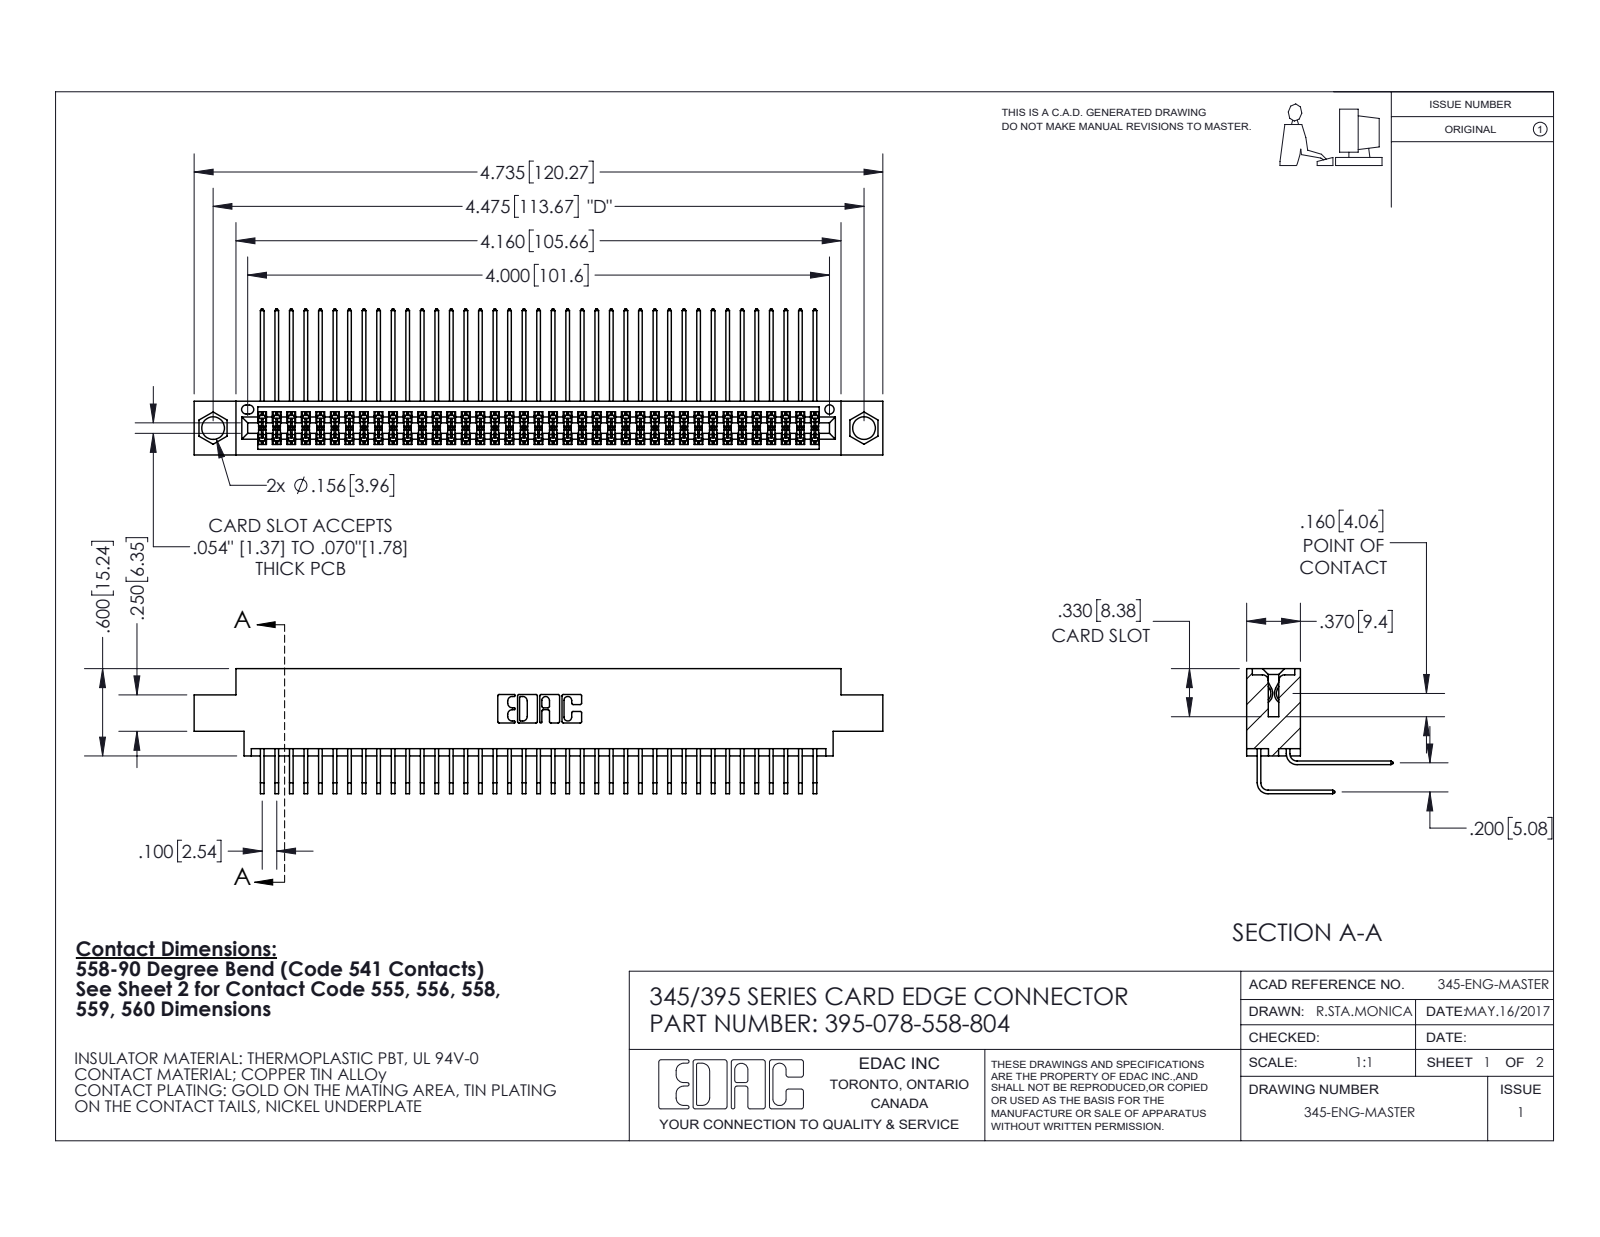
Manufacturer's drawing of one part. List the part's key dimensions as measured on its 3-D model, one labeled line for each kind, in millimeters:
Part name (STEP PRODUCT): 395-078-558-804; 345 Part_0.170 Offset - 0.156 Dia-TI; 345-292-001_558 559 Tail - 1; 345-292-001_558 Tail - 2
STEP written by: SolidWorks 2020 (CONFIG_CONTROL_DESIGN)
Units: millimetres
Bodies: 79 solids, 4200 faces (2828 planar, 1372 cylindrical, 0 other)
Overall size (bounding box): 120.3 × 25.5 × 21.8
Volume: 11 900 mm³ · Surface area: 19 620 mm²
Round holes (diameter × count): ⌀4 ×2, ⌀1.6 ×1
Partial cylindrical surfaces — rounded edges, fillets, slot ends (radius × count): R0.2 ×117, R0.3 ×22, R0.2 ×6, R0.8 ×6, R0.7 ×3, R0.4 ×2, R0.5 ×2, R0.6 ×2
Main face-to-face distances: 1.8, 7.6, 5.1, 9.4, 2.5, 6.9, 0.6, 5.7, 4.4, 0.6
Hole centre spacings: 6.9, 107.7, 113.7
